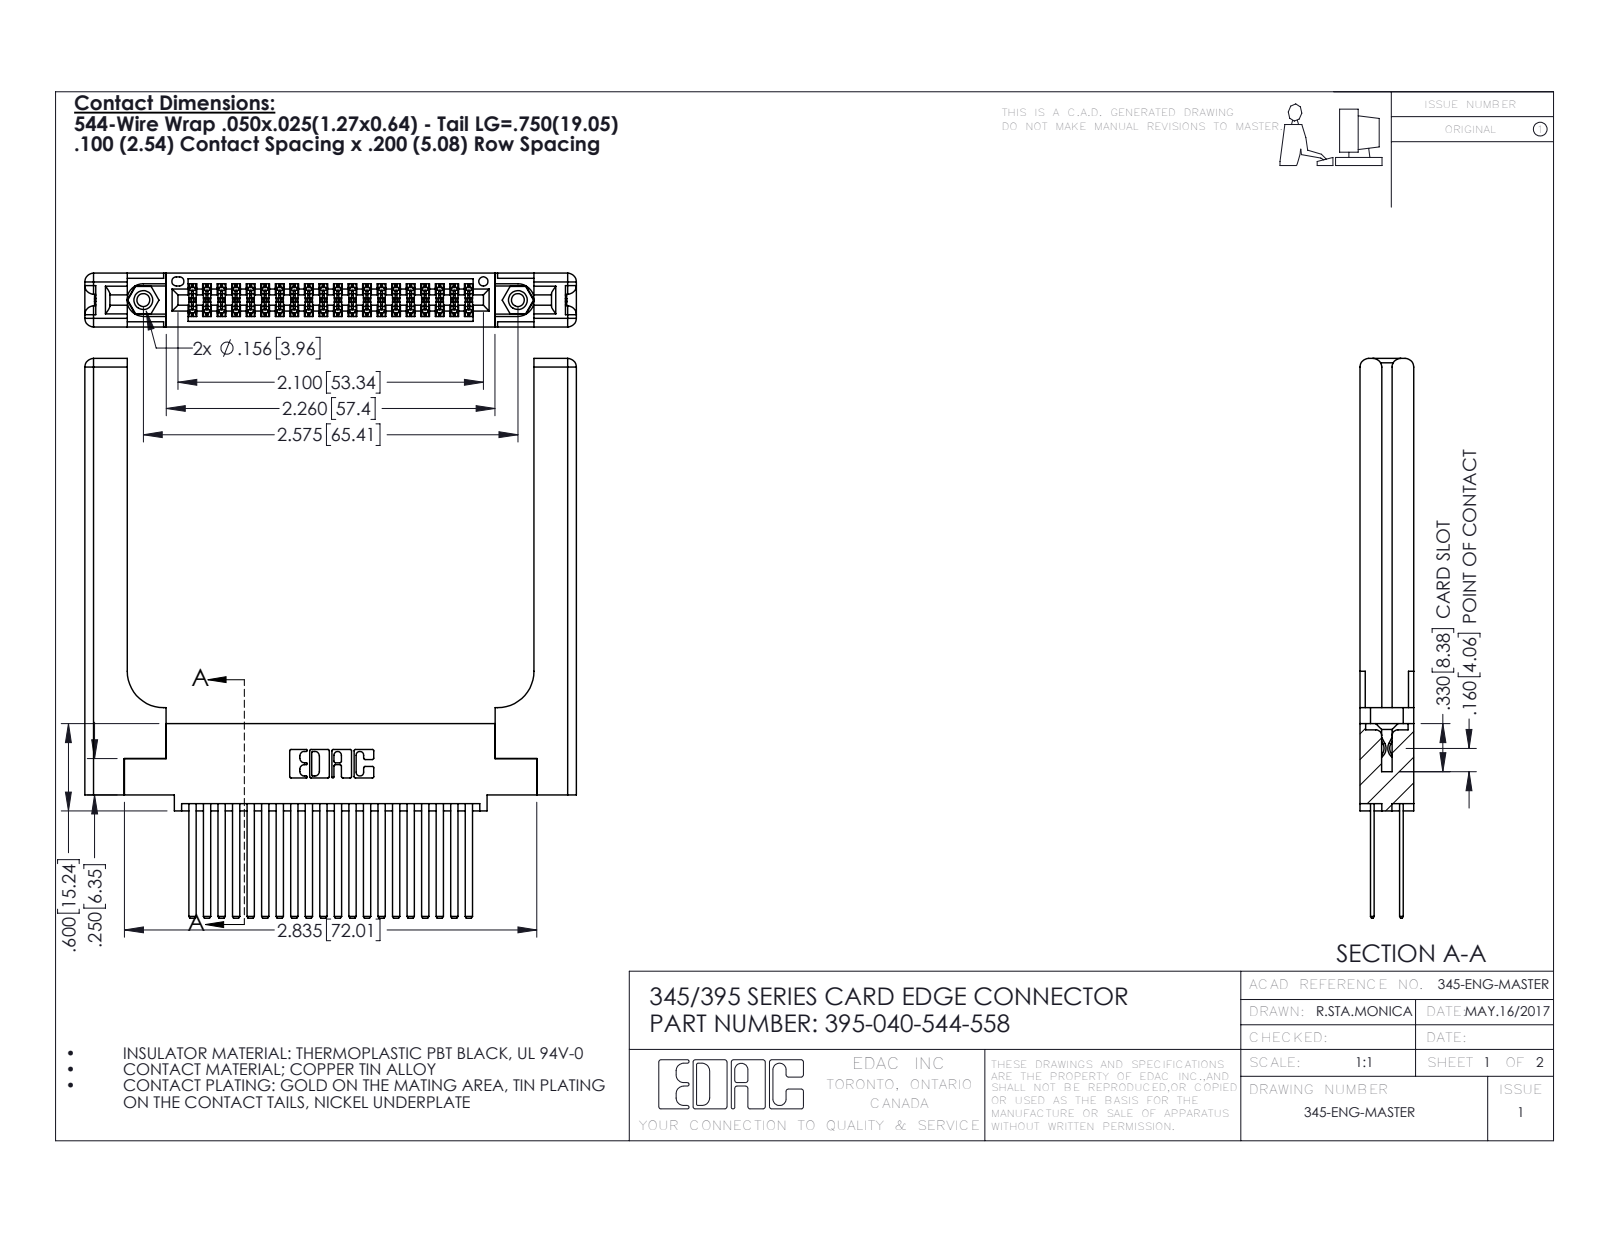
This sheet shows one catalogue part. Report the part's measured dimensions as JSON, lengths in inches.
{"part_name": "345-292-001_345-293-144; 345 Part_0.110 Offset - 0.156 Dia-TH; 345-220-058_345-220-058; 345-250-001_345-250-001-102 (+1 more)", "step_written_by": "SolidWorks 2016 (CONFIG_CONTROL_DESIGN)", "units": "inches", "bodies": {"solids": 45, "faces": 2146, "planar": 1392, "cylindrical": 694, "other": 60}, "overall_size": [3.847, 3.379, 0.37], "volume_in3": 1.043, "surface_area_in2": 29.62, "round_holes": [[0.089, 2], [0.125, 2], [0.156, 2], [0.064, 1]], "round_bosses_or_shafts": [[0.155, 2]], "partial_cylinders_radius": [[0.006, 60], [0.01, 22], [0.06, 16], [0.007, 6], [0.031, 6], [0.026, 3], [0.014, 2], [0.019, 2]], "face_to_face_distances": [0.072, 0.298, 0.37, 0.098, 0.272, 0.025, 0.2, 0.225, 0.148, 0.15], "hole_center_spacings": [0.27, 2.341, 2.575]}
